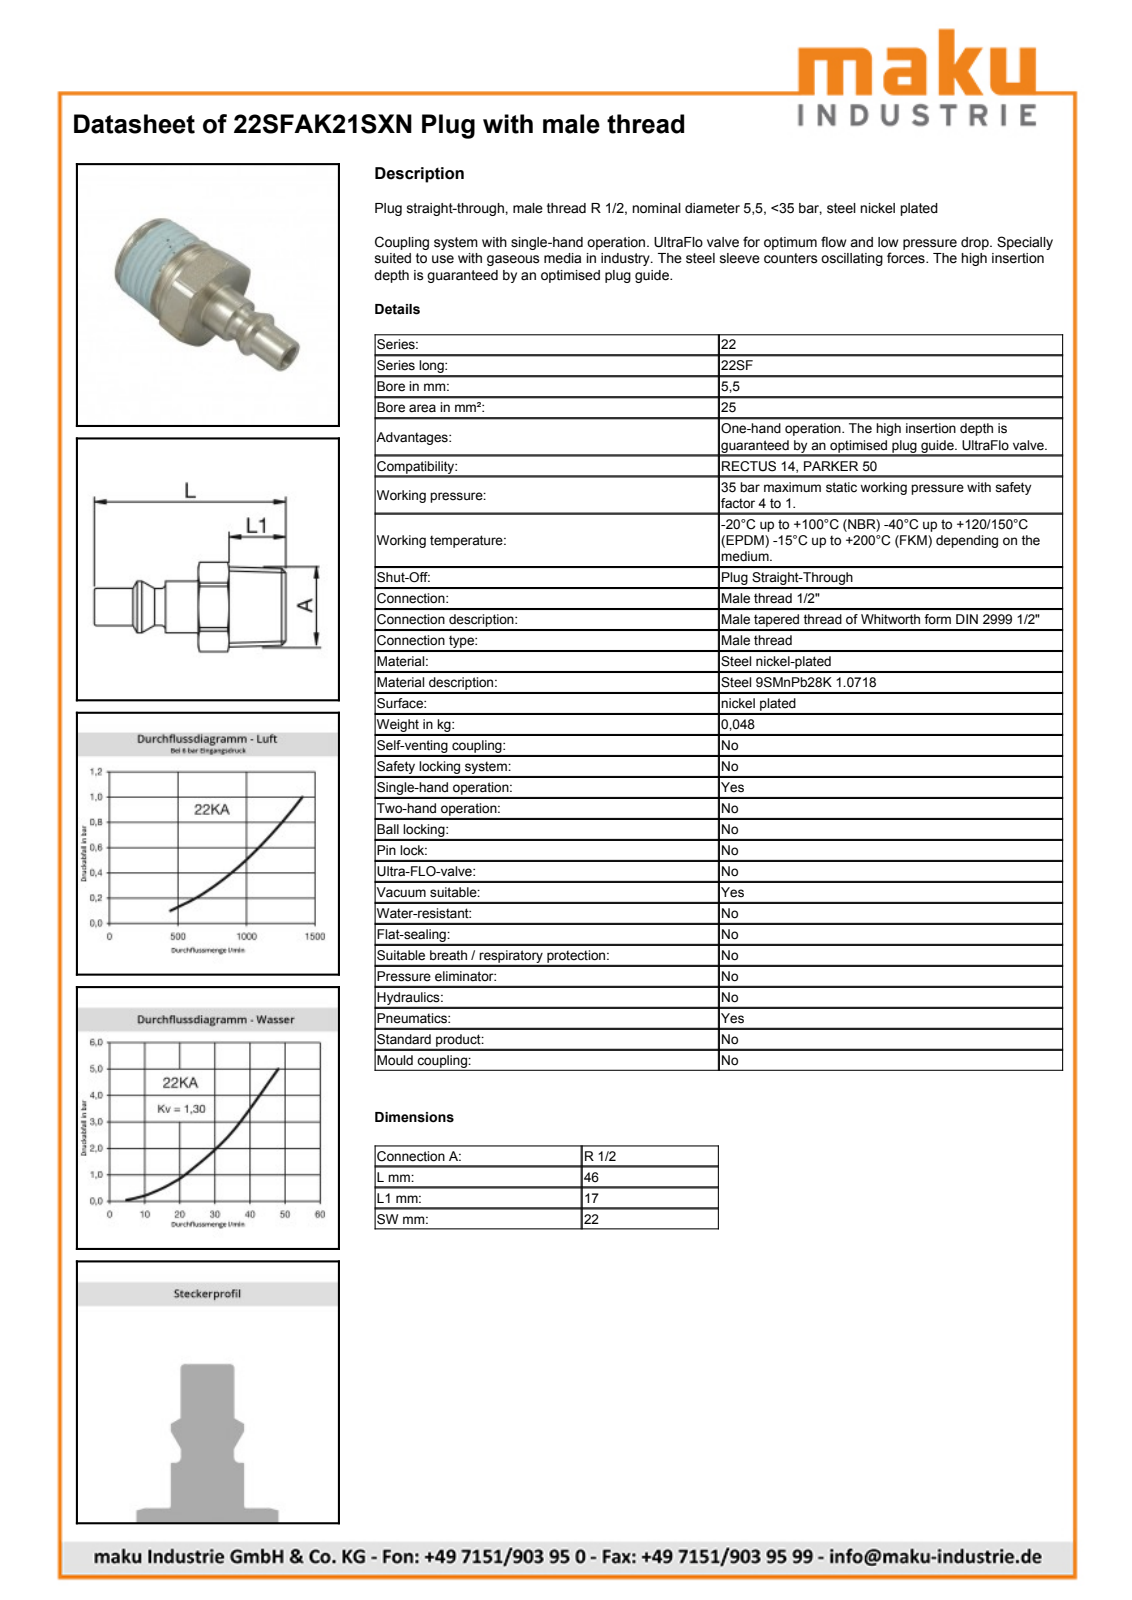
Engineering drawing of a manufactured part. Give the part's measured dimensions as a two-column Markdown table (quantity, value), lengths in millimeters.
| quantity | value |
| --- | --- |
| part name | D113546 |
| STEP written by | Autodesk Inventor 2013 (AUTOMOTIVE_DESIGN) |
| units | millimeters |
| bodies | 1 solid, 43 faces (11 planar, 12 cylindrical, 20 other) |
| overall size | 46 × 24.8 × 22 |
| volume | 5 655 mm³ |
| surface area | 4 119 mm² |
| round holes (diameter × count) | 5.5 × 1, 13 × 1 |
| round bosses / shafts (diameter × count) | 10.9 × 1, 7.9 × 1, 7.8 × 1 |
| partial cylindrical surfaces (radius × count) | 12.4 × 1 |
| main face-to-face distances | 22, 7, 24, 17, 6.93, 13.93, 30.93, 15.07, 29, 46 |
